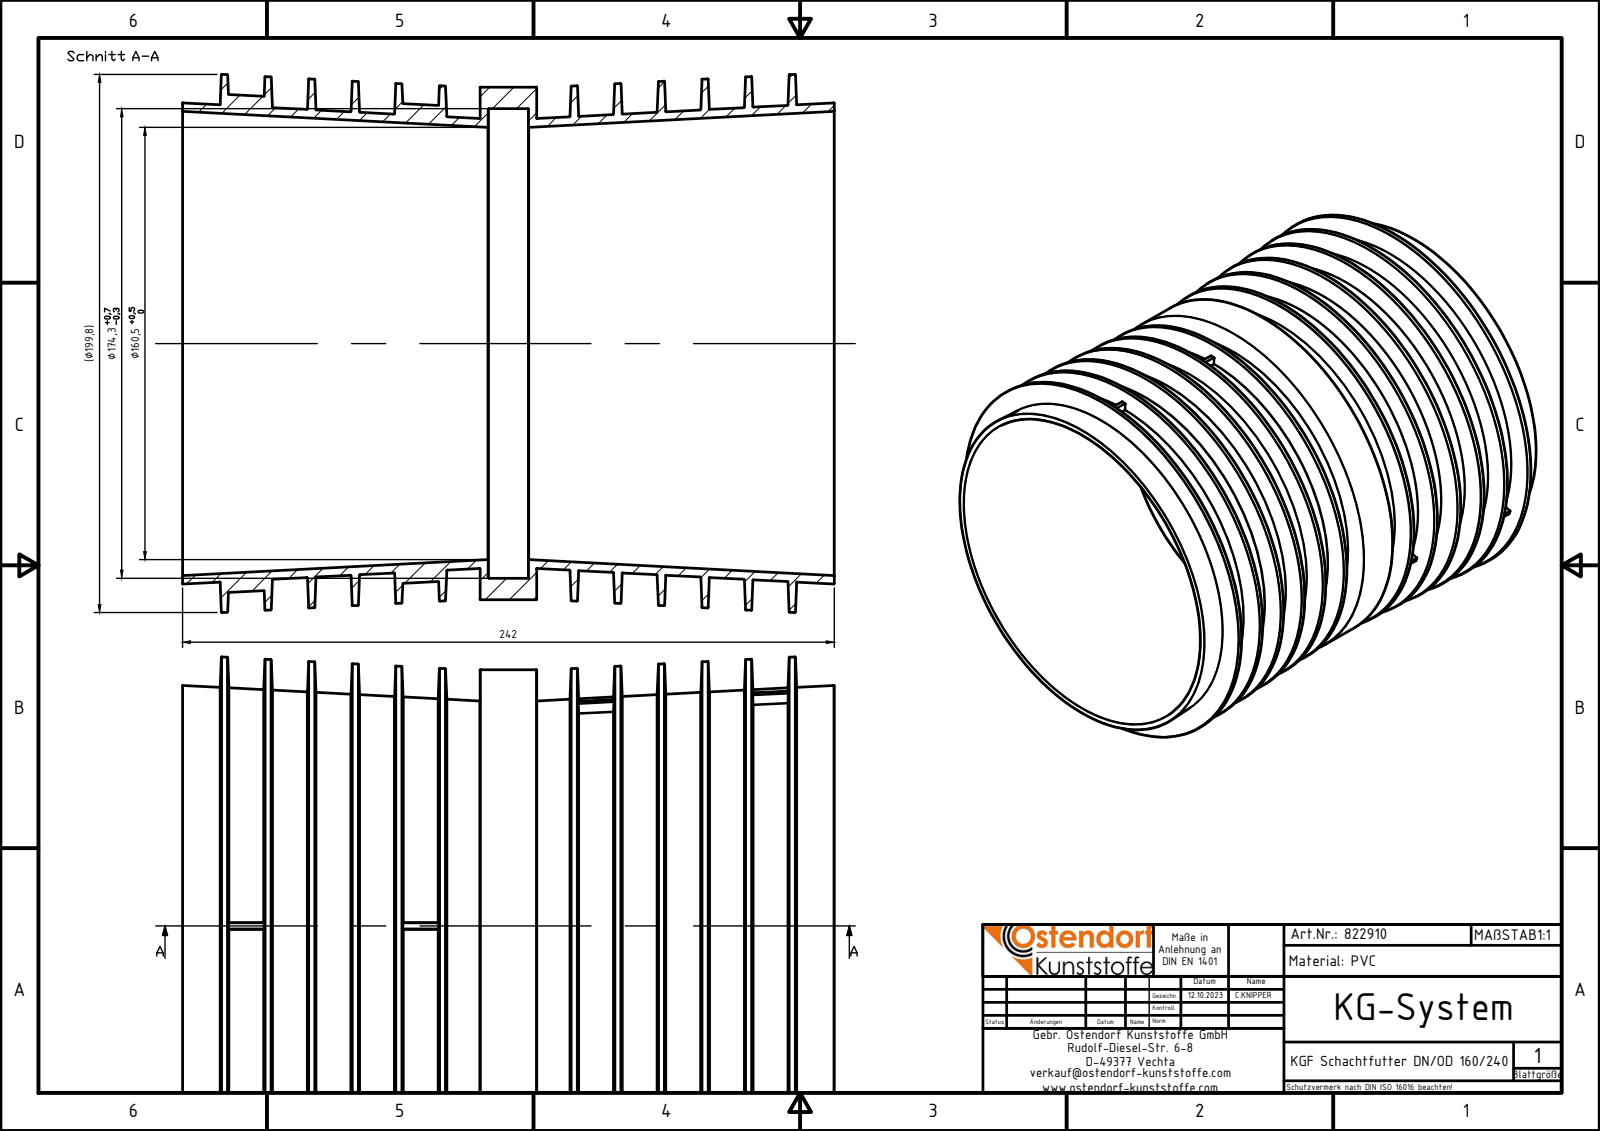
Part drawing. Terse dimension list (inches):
name: 822910z
written by: Autodesk Inventor 2024 (AUTOMOTIVE_DESIGN)
unit: in
bodies: 1 solid, 284 faces (30 planar, 18 cylindrical, 236 other)
size: 9.528 × 7.865 × 7.865
volume: 42.72 in³; area: 674.7 in²
holes: 1× ⌀6.862
bosses: 1× ⌀7.492
rounds: 16× R0.008
face distances: 0.118, 0.709, 0.827, 0.591, 4.35, 4.469, 5.059, 5.177, 9.528, 0.094
